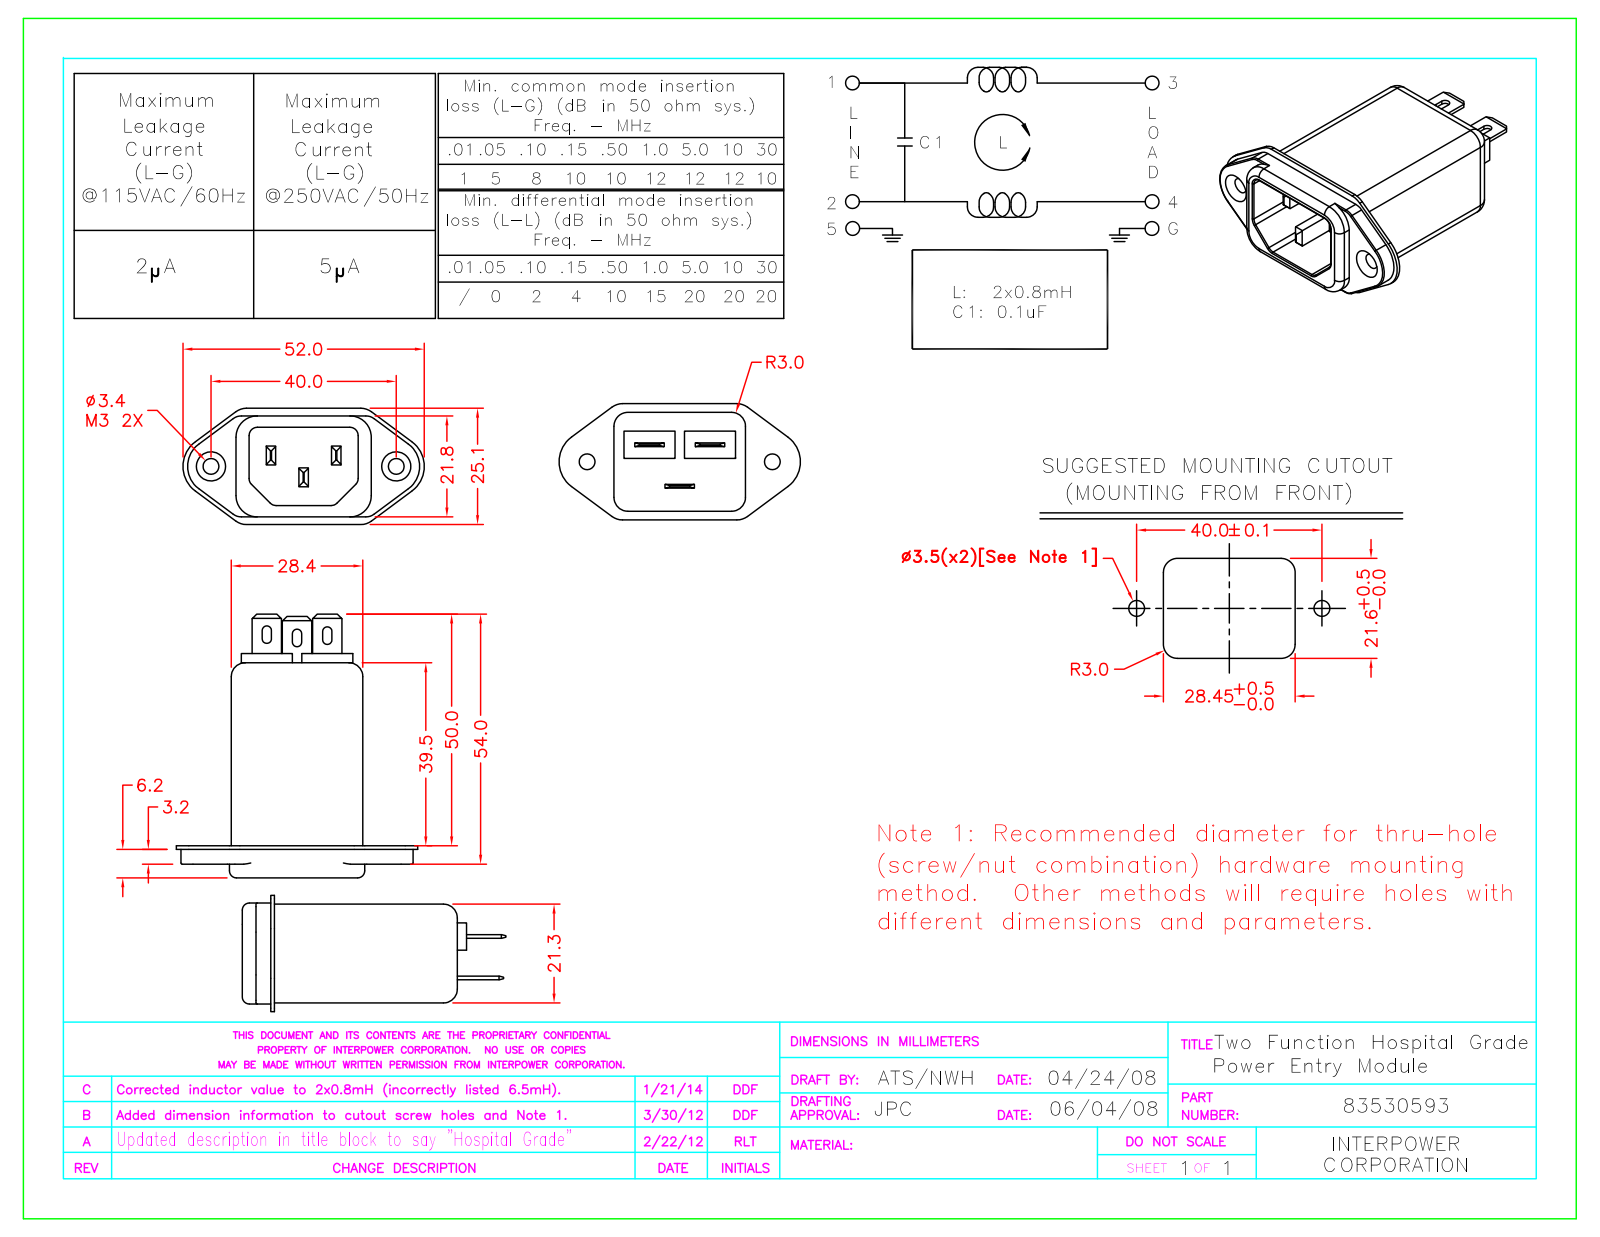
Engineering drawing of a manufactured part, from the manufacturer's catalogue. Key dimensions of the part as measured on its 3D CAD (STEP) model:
Part name (STEP PRODUCT): 06GEEG3EM
STEP written by: SolidWorks 2008 (CONFIG_CONTROL_DESIGN)
Units: inches
Bodies: 1 solid, 188 faces (103 planar, 60 cylindrical, 25 other)
Overall size (bounding box): 2.241 × 2.051 × 0.988
Volume: 1.432 in³ · Surface area: 13.38 in²
Round holes (diameter × count): ⌀0.134 ×2
Partial cylindrical surfaces — rounded edges, fillets, slot ends (radius × count): R0.01 ×12, R0.118 ×12, R0.039 ×6, R0.071 ×6, R0.059 ×4, R0.151 ×4, R0.181 ×4, R0.236 ×2
Main face-to-face distances: 0.84, 1.118, 0.087, 0.753, 0.378, 0.095, 1.023, 0.156, 1.178, 1.555
Hole centre spacings: 1.575
